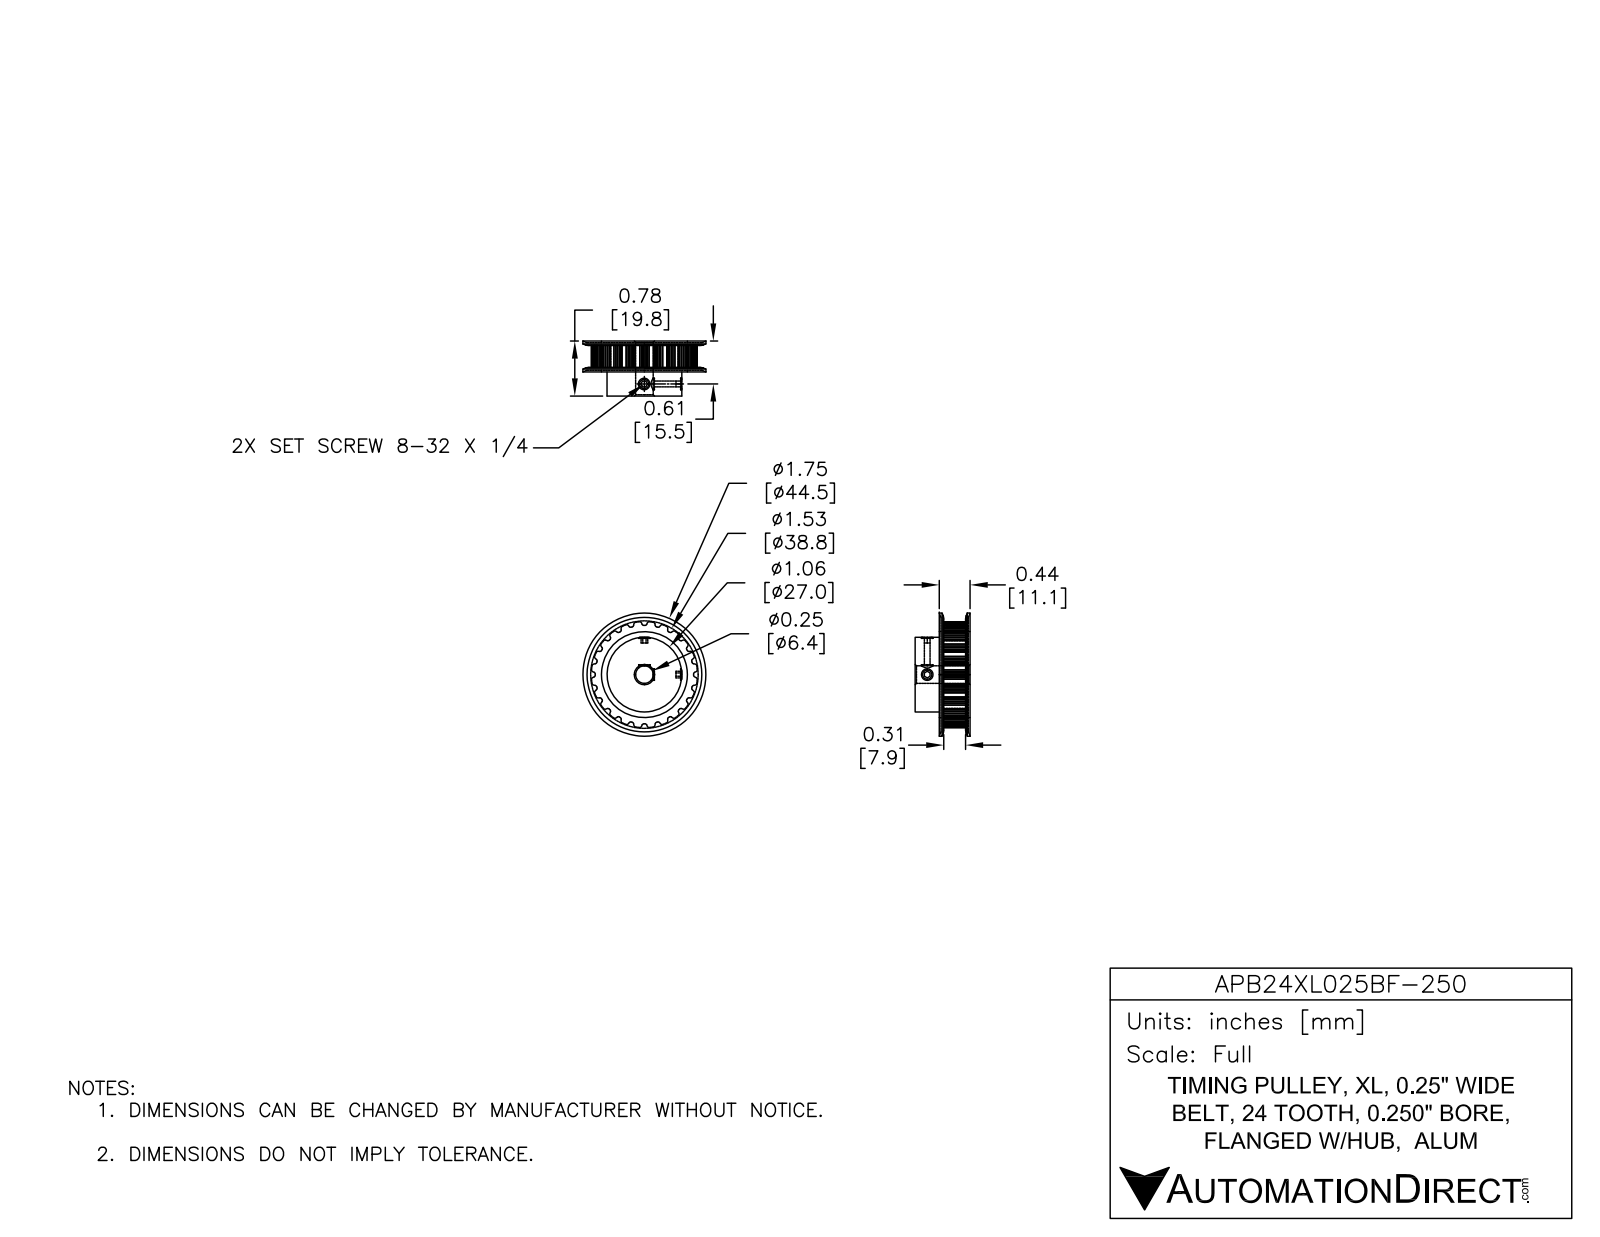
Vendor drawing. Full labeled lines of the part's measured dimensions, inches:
Part name (STEP PRODUCT): APB24XL025BF-250
STEP written by: SolidWorks 2014 (AUTOMOTIVE_DESIGN)
Units: inches
Bodies: 1 solid, 245 faces (78 planar, 145 cylindrical, 22 other)
Overall size (bounding box): 1.75 × 1.75 × 0.781
Volume: 0.996 in³ · Surface area: 10.53 in²
Round holes (diameter × count): ⌀0.088 ×2, ⌀0.25 ×1
Round bosses / shafts (diameter × count): ⌀1.063 ×1
Partial cylindrical surfaces — rounded edges, fillets, slot ends (radius × count): R0.015 ×96, R0.699 ×1
Main face-to-face distances: 0.375, 0.033, 0.407, 0.781, 0.748, 0.374, 0.032, 0.343, 1.508, 0.546
